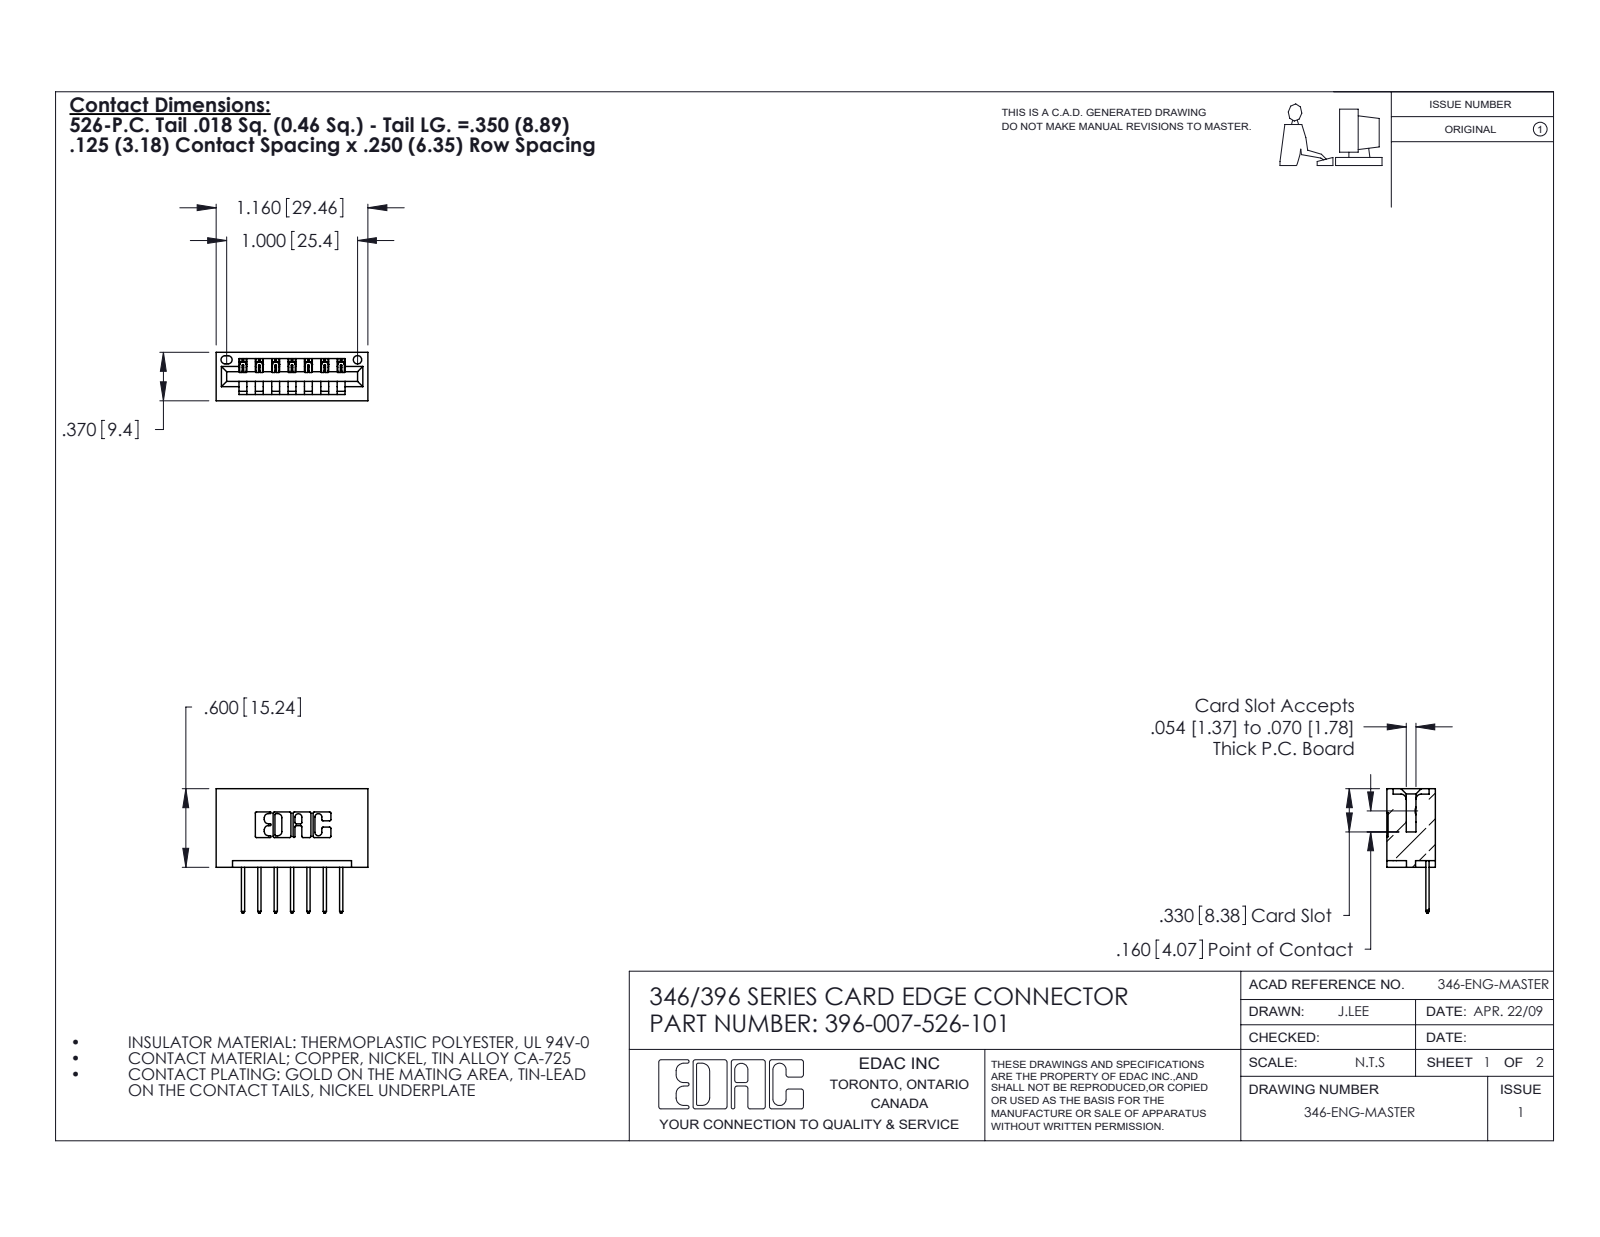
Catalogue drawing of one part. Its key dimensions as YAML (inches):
part_name: "346 Part_No Mounting Lugs; 345-292-001_345-293-126; 396-007-526-101"
step_written_by: "SolidWorks 2020 (CONFIG_CONTROL_DESIGN)"
units: inches
bodies: {solids: 8, faces: 520, planar: 352, cylindrical: 168, other: 0}
overall_size: [1.16, 0.95, 0.37]
volume: 0.191
surface_area: 5.571
round_holes:
  - {diameter: 0.064, count: 1}
partial_cylinders:
  - {radius: 0.01, count: 22}
  - {radius: 0.006, count: 14}
  - {radius: 0.01, count: 14}
  - {radius: 0.007, count: 6}
  - {radius: 0.031, count: 6}
  - {radius: 0.026, count: 3}
  - {radius: 0.031, count: 2}
  - {radius: 0.04, count: 2}
face_to_face_distances: [0.25, 0.048, 0.322, 0.37, 0.125, 0.148, 0.222, 0.1, 0.174, 0.072]
